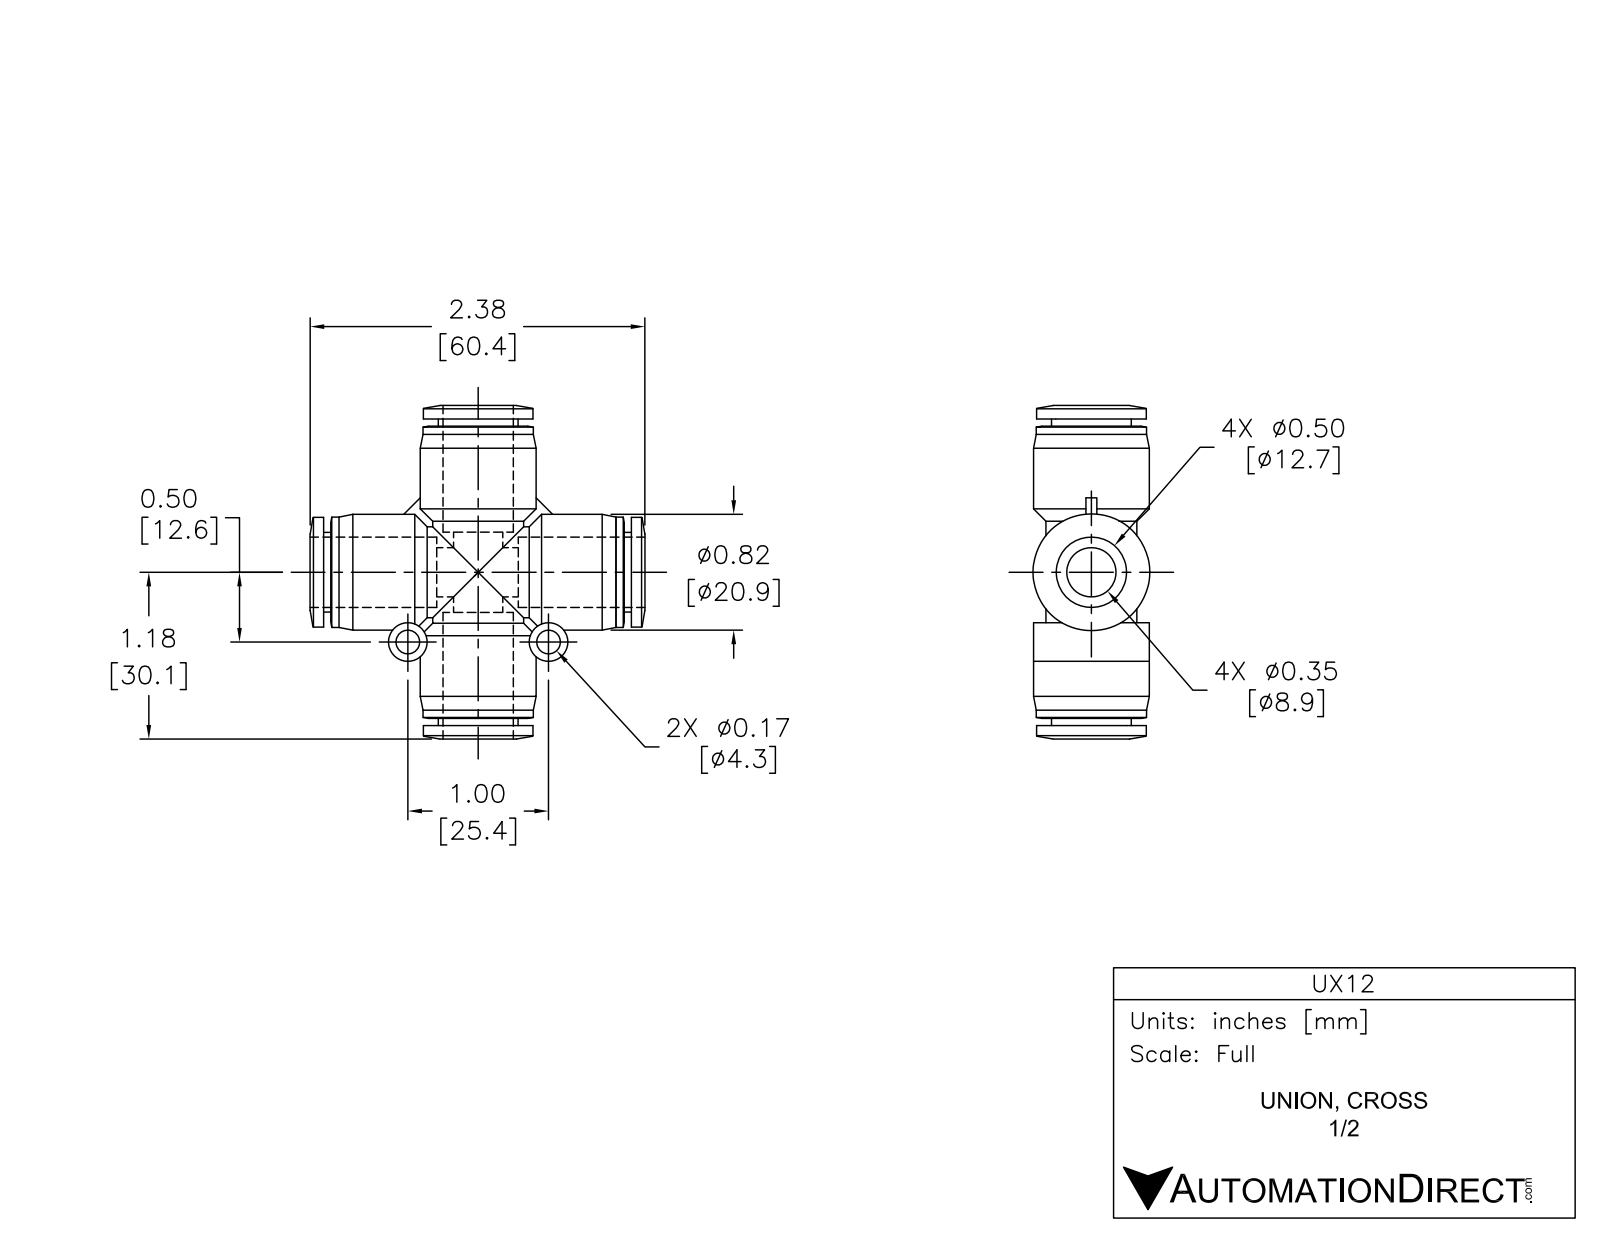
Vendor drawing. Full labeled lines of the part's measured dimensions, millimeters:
Part name (STEP PRODUCT): UX12
STEP written by: SolidWorks 2015 (AUTOMOTIVE_DESIGN)
Units: millimetres
Bodies: 1 solid, 149 faces (26 planar, 65 cylindrical, 58 other)
Overall size (bounding box): 60.5 × 60.5 × 21
Volume: 18 710 mm³ · Surface area: 13 750 mm²
Round holes (diameter × count): ⌀4.3 ×2, ⌀10 ×2, ⌀13 ×2
Round bosses / shafts (diameter × count): ⌀21 ×2, ⌀20 ×2, ⌀19.9 ×2, ⌀16.5 ×2, ⌀14.5 ×2, ⌀7 ×2
Main face-to-face distances: 54.3, 1.3, 55.6, 20.7, 35, 19.4, 33.7, 53, 14.3, 9.5
Hole centre spacings: 25.1
